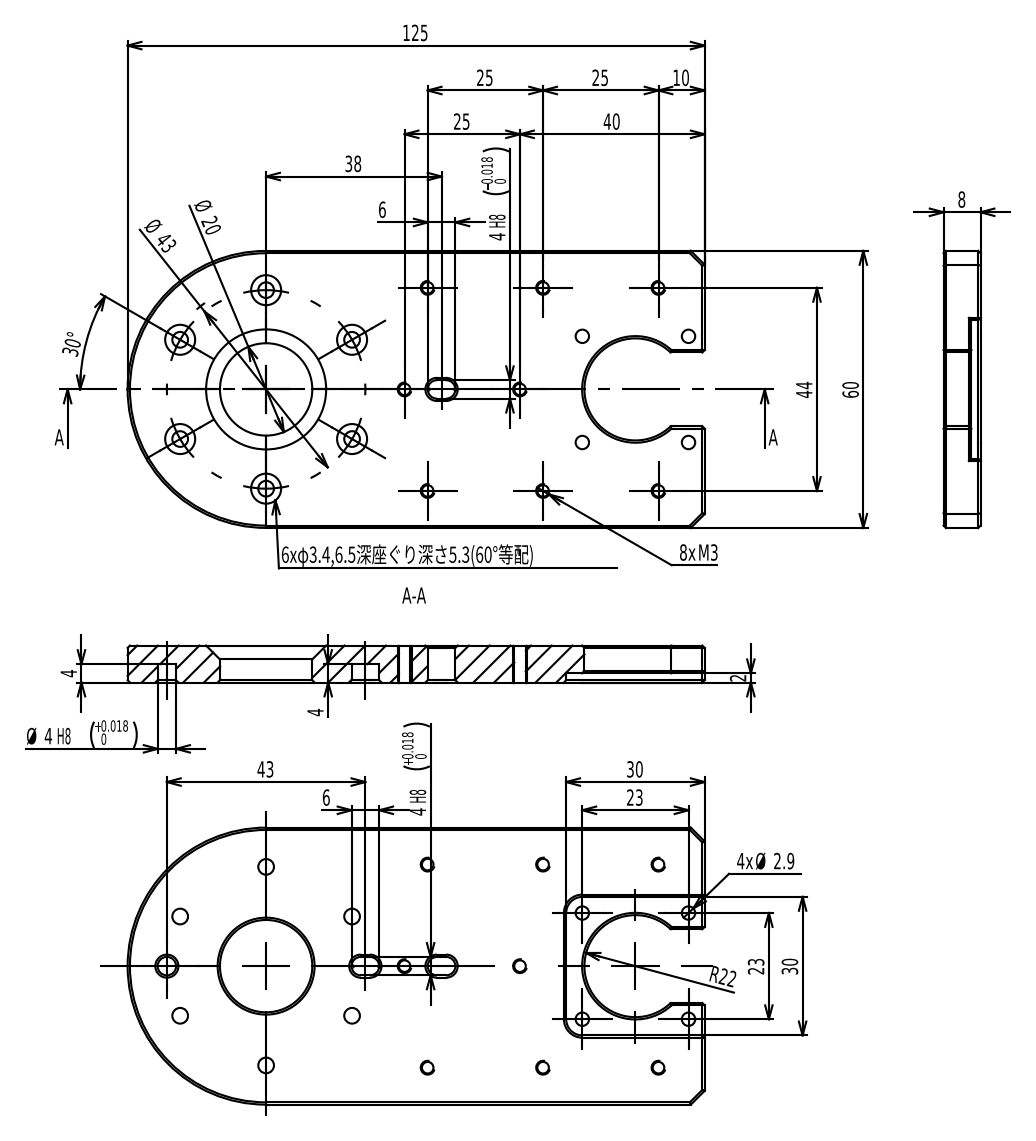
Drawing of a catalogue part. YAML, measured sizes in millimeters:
part_name: "PDG60-34"
step_written_by: "SolidWorks 2020 (CONFIG_CONTROL_DESIGN)"
units: millimeters
bodies: {solids: 1, faces: 148, planar: 63, cylindrical: 62, other: 23}
overall_size: [125, 60, 8]
volume: 47343
surface_area: 17416
round_holes:
  - {diameter: 2.5, count: 8}
  - {diameter: 3.4, count: 6}
  - {diameter: 6.5, count: 6}
  - {diameter: 2.9, count: 4}
  - {diameter: 4, count: 1}
  - {diameter: 20, count: 1}
partial_cylinders:
  - {radius: 2, count: 4}
  - {radius: 3.5, count: 2}
  - {radius: 11.05, count: 1}
  - {radius: 30, count: 1}
face_to_face_distances: [8, 60, 6, 2, 5.3, 0.7, 2.7, 47.37, 4, 15]
hole_center_spacings: [21.5, 37.24, 25, 22.56, 23, 37.2, 50.61, 43]
